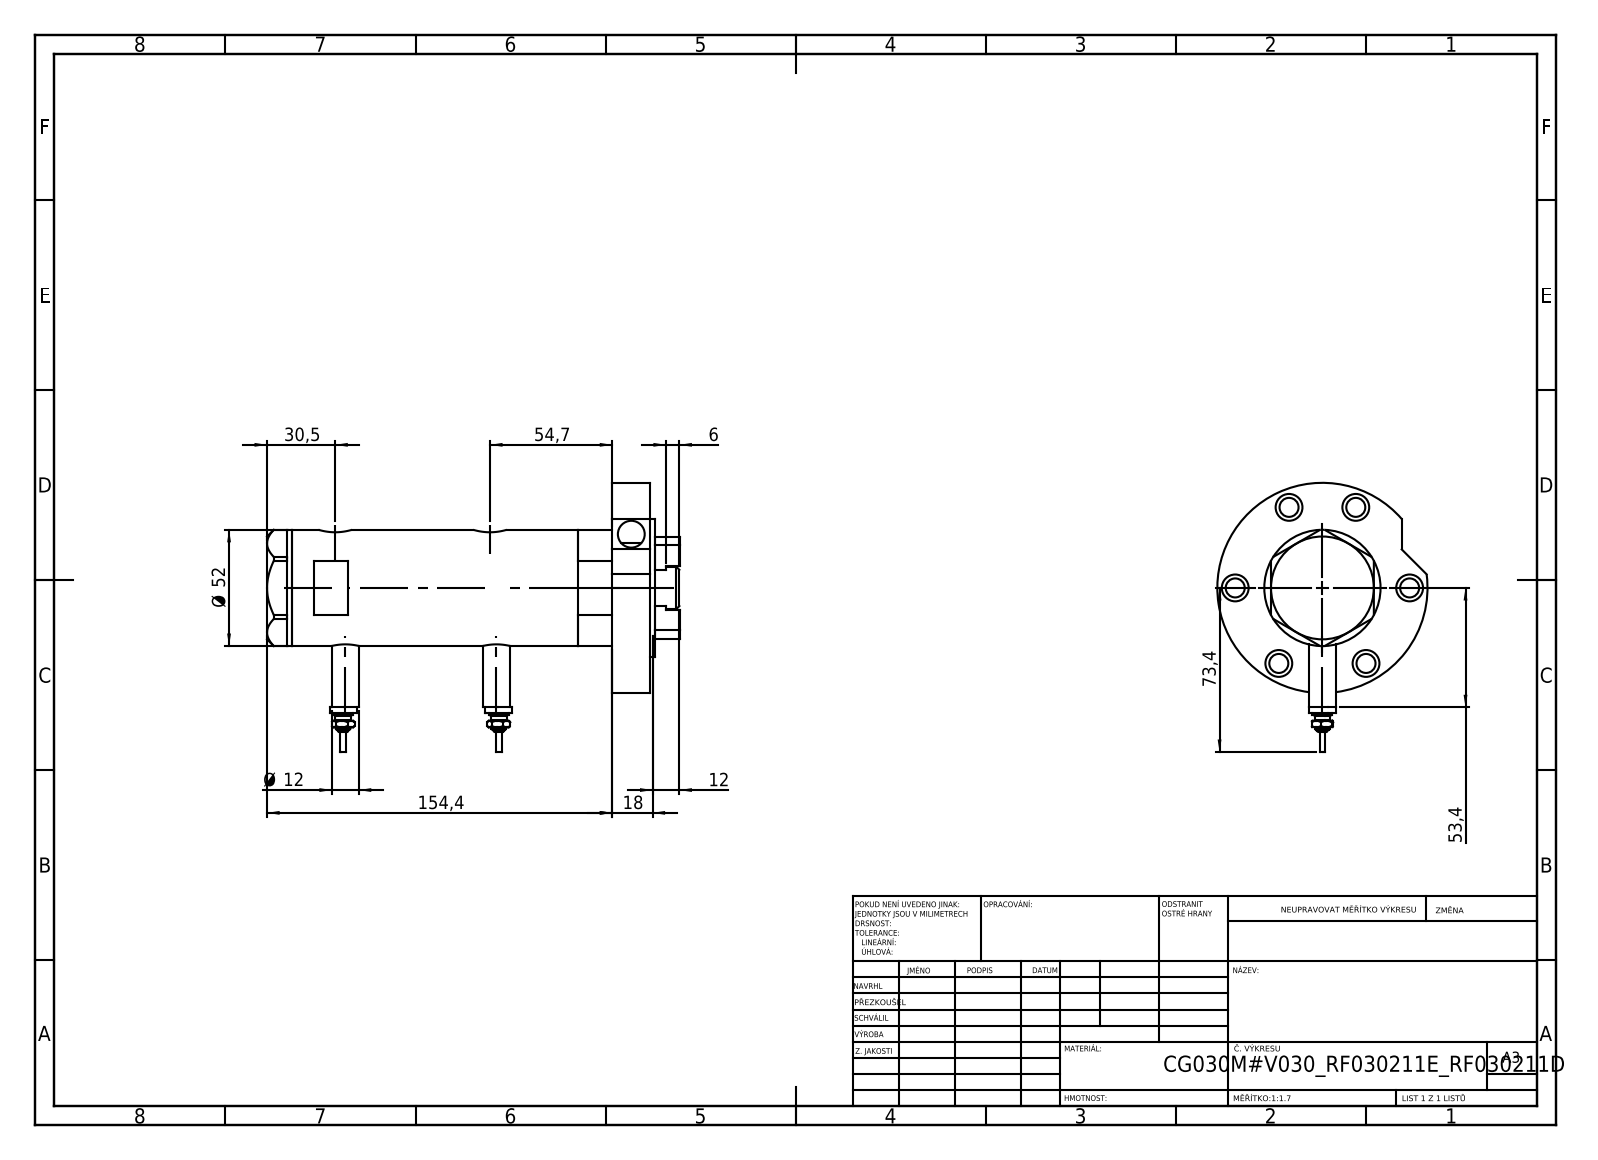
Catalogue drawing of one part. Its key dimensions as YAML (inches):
part_name: "V270CG_RF211E; V270CG_VC; V270CG_RF211D; Switch (+3 more)"
step_written_by: "SolidWorks 2019 (CONFIG_CONTROL_DESIGN)"
units: inches
bodies: {solids: 9, faces: 310, planar: 128, cylindrical: 118, other: 64}
overall_size: [7.268, 4.74, 3.701]
volume: 26.06
surface_area: 166
round_holes:
  - {diameter: 0.472, count: 7}
  - {diameter: 0.335, count: 6}
  - {diameter: 0.201, count: 4}
  - {diameter: 0.354, count: 4}
  - {diameter: 0.383, count: 2}
  - {diameter: 0.492, count: 2}
  - {diameter: 0.591, count: 2}
  - {diameter: 0.256, count: 1}
  - {diameter: 0.787, count: 1}
  - {diameter: 0.846, count: 1}
  - {diameter: 1.181, count: 1}
  - {diameter: 1.299, count: 1}
round_bosses_or_shafts:
  - {diameter: 0.472, count: 4}
  - {diameter: 0.354, count: 2}
  - {diameter: 0.276, count: 2}
  - {diameter: 0.177, count: 2}
  - {diameter: 0.098, count: 2}
  - {diameter: 3.701, count: 1}
  - {diameter: 2.441, count: 1}
  - {diameter: 2.047, count: 1}
face_to_face_distances: [0.669, 5.646, 6.315, 0.079, 0.433, 6.394, 3.602, 2.043, 2.713, 6.827]
hole_center_spacings: [1.535, 0.659, 1.479, 1.843, 0.394, 0.881, 0.904, 1.113]
